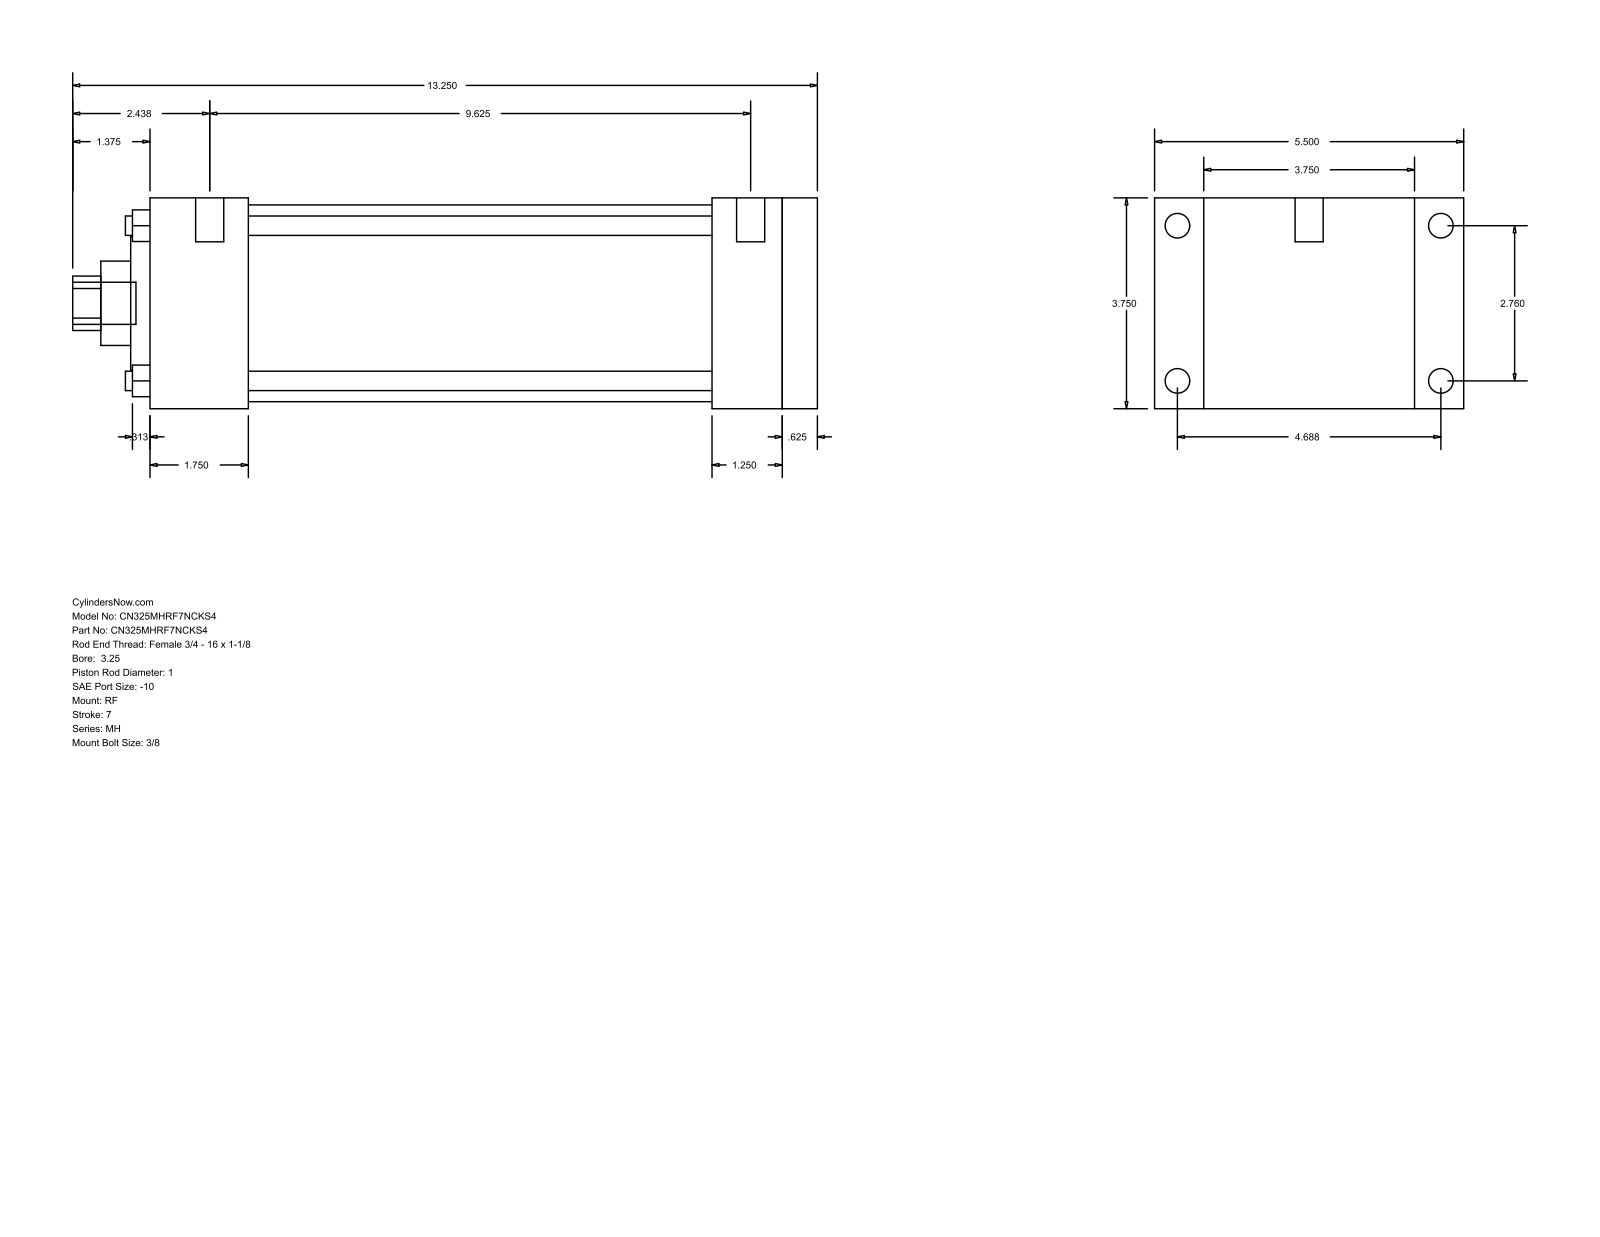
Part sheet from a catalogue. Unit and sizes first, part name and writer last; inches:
Units: inches
Overall size (bounding box): 13.25 × 5.5 × 3.75
Round holes (diameter × count): ⌀0.345 ×4, ⌀1 ×1, ⌀1.5 ×1, ⌀2.375 ×1, ⌀3.5 ×1
Round bosses / shafts (diameter × count): ⌀0.438 ×4, ⌀0.219 ×4, ⌀0.5 ×2, ⌀0.75 ×1
Partial cylindrical surfaces — rounded edges, fillets, slot ends (radius × count): R0.484 ×1
Main face-to-face distances: 3.75, 11.875, 0.625, 11.25, 0.875, 4.625, 1.75, 9.5, 10.125, 10
Hole centre spacings: 1.952, 2.76, 3.903
Bodies: 0 solids, 94 faces (65 planar, 29 cylindrical, 0 other)
Part name (STEP PRODUCT): MH_RF__0325_1
STEP written by: GSSL Pune (CONFIG_CONTROL_DESIGN)
